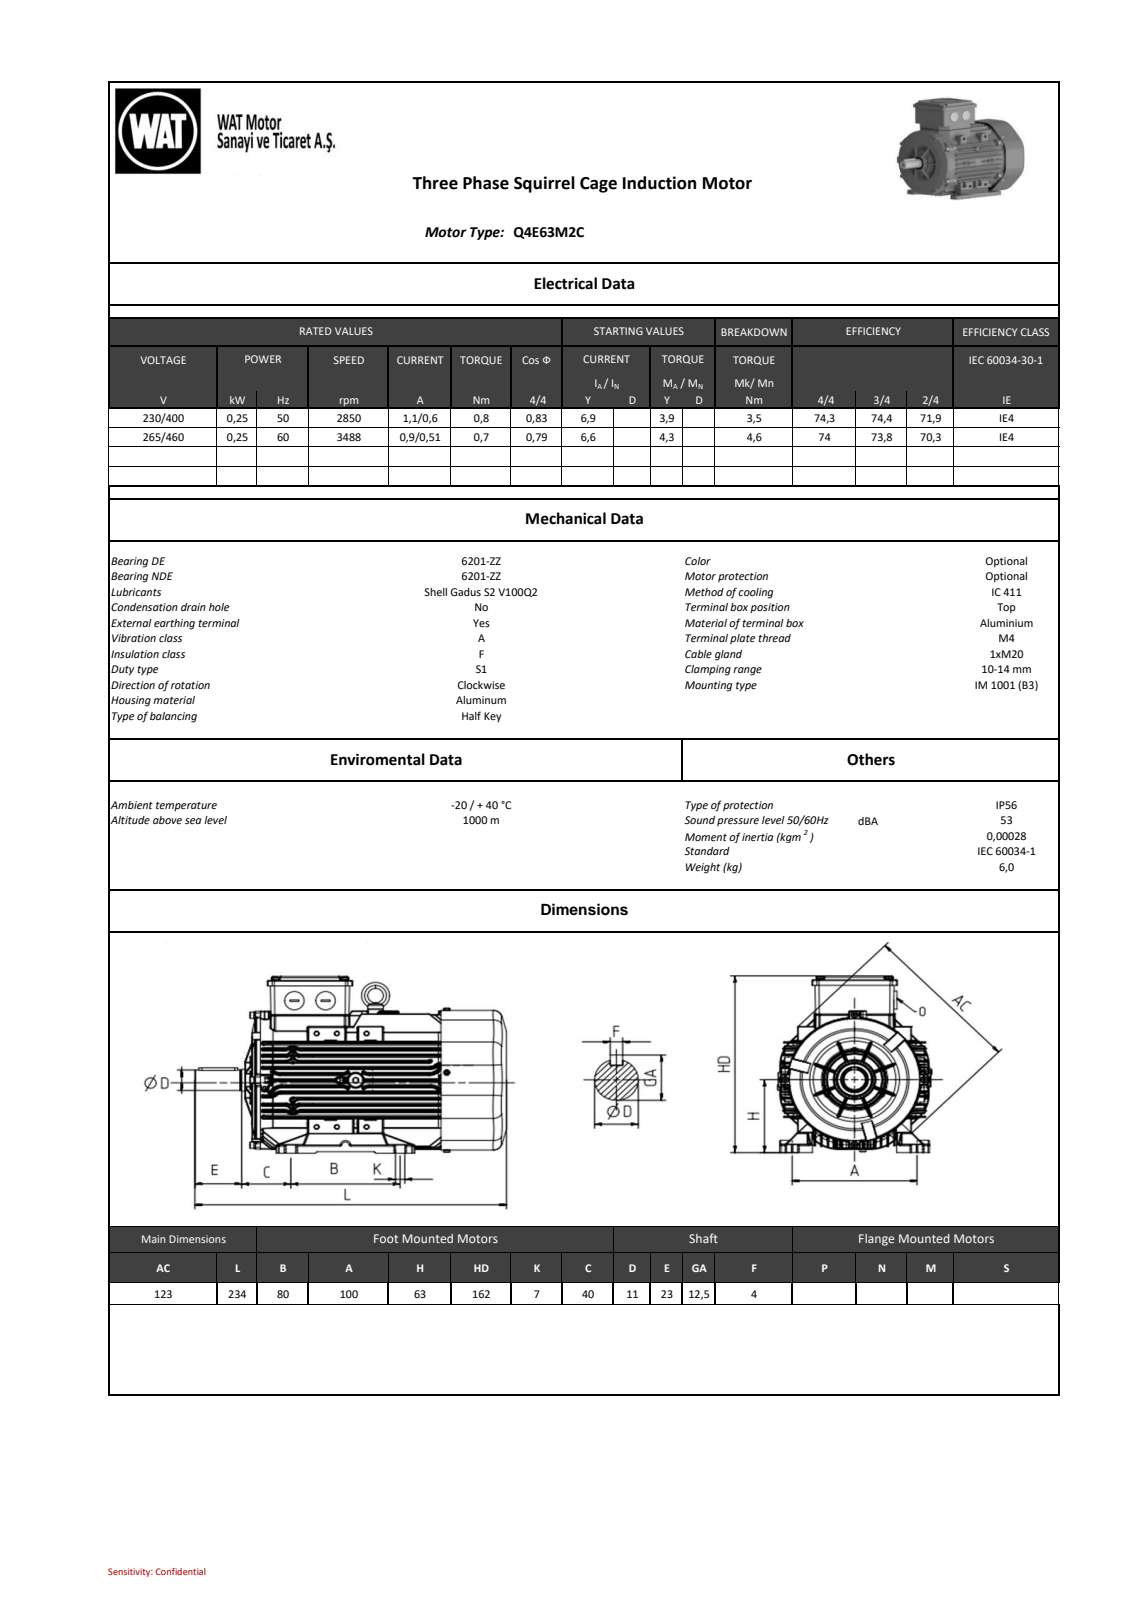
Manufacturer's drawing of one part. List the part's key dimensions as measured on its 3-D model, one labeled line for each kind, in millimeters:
Part name (STEP PRODUCT): QE Series_ 63_B3_Deep Cover__stp_objects
STEP written by: SIEMENS PLM Software NX2206.8101 (AP203_CONFIGURATION_CONTROLLED_3D_DESIGN_OF_MECHANICAL_PARTS_AND_ASSEMBLIES_MIM_LF)
Units: millimetres
Bodies: 0 solids, 1449 faces (835 planar, 448 cylindrical, 166 other)
Overall size (bounding box): 233.47 × 162.1 × 126.28
Round holes (diameter × count): ⌀2.5 ×4, ⌀3.65 ×4, ⌀4.2 ×4, ⌀4.8 ×4, ⌀3 ×3, ⌀7 ×2, ⌀5 ×1, ⌀8 ×1, ⌀14.96 ×1, ⌀19 ×1, ⌀19.84 ×1, ⌀57 ×1
Round bosses / shafts (diameter × count): ⌀8 ×8, ⌀123 ×1, ⌀61 ×1, ⌀30 ×1, ⌀25.28 ×1, ⌀12 ×1, ⌀11 ×1
Partial cylindrical surfaces — rounded edges, fillets, slot ends (radius × count): R1 ×107, R0.5 ×104, R1.5 ×16, R2 ×16, R4 ×8, R8 ×6, R0.1 ×5, R0.3 ×5
Main face-to-face distances: 5, 7.02, 27.96, 10.5, 28.05, 7, 6.93, 13.81, 114.5, 6.88
Hole centre spacings: 54, 54.45, 77, 10, 5, 31.5, 31.52, 31.89
